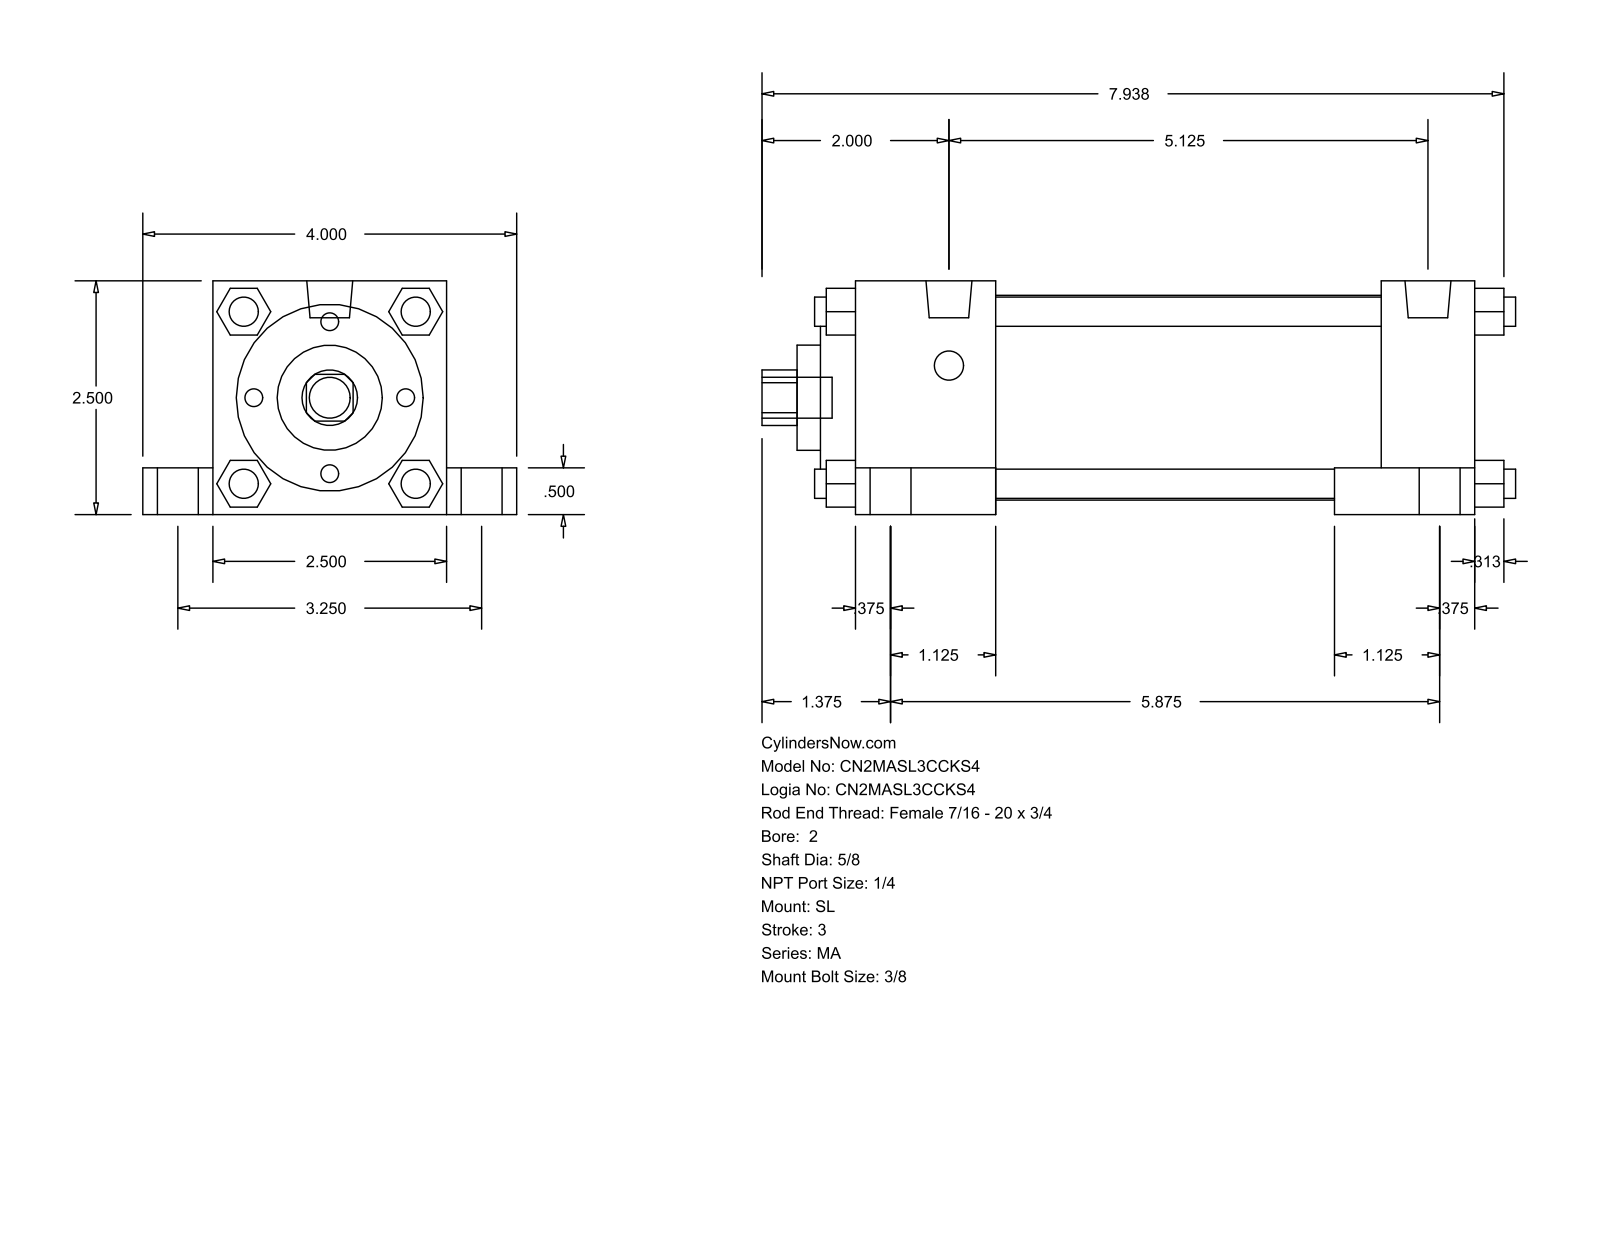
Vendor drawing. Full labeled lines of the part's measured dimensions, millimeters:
Part name (STEP PRODUCT): MA_SL__0200_0.625
STEP written by: GSSL Pune (CONFIG_CONTROL_DESIGN)
Units: millimetres
Bodies: 0 solids, 150 faces (113 planar, 37 cylindrical, 0 other)
Overall size (bounding box): 204.79 × 101.6 × 63.5
Round holes (diameter × count): ⌀15.88 ×1, ⌀28.57 ×1, ⌀50.8 ×1, ⌀55.63 ×1
Round bosses / shafts (diameter × count): ⌀7.94 ×8, ⌀11.11 ×5, ⌀17.46 ×4, ⌀12.49 ×2
Partial cylindrical surfaces — rounded edges, fillets, slot ends (radius × count): R7.54 ×1
Main face-to-face distances: 63.5, 12.7, 9.52, 25.4, 19.05, 82.55, 38.1, 168.28, 50.8, 130.18
